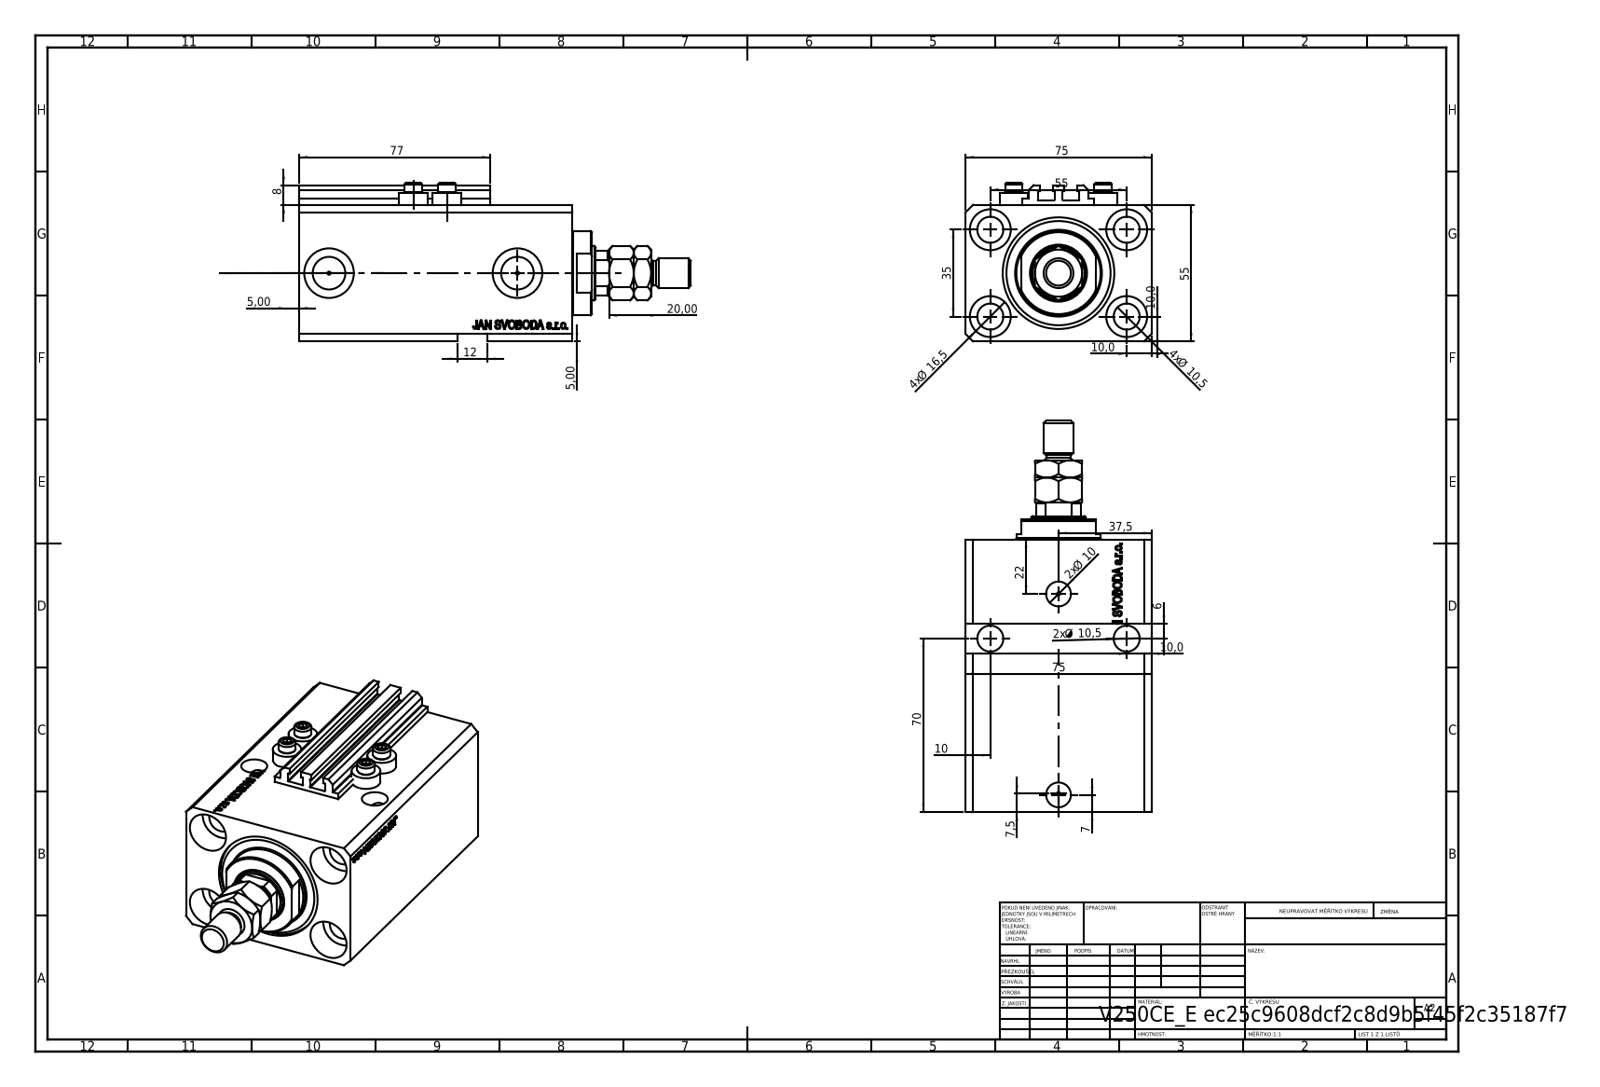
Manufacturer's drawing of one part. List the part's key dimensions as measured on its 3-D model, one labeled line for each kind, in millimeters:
Part name (STEP PRODUCT): V250CE_E; V250CE_C_VCP; ALLEN BOLT V250CE; V250CE_VC_E (+1 more)
STEP written by: SolidWorks 2019 (CONFIG_CONTROL_DESIGN)
Units: millimetres
Bodies: 9 solids, 1113 faces (529 planar, 130 cylindrical, 454 other)
Overall size (bounding box): 157.9 × 75 × 64
Volume: 394 729 mm³ · Surface area: 99 045 mm²
Round holes (diameter × count): ⌀10.5 ×7, ⌀1.25 ×4, ⌀4 ×4, ⌀16.5 ×4, ⌀10 ×2, ⌀13.16 ×2, ⌀20 ×2, ⌀22 ×1, ⌀32 ×1, ⌀45 ×1
Round bosses / shafts (diameter × count): ⌀11.6 ×4, ⌀7 ×4, ⌀34 ×1, ⌀12 ×1, ⌀10 ×1
Partial cylindrical surfaces — rounded edges, fillets, slot ends (radius × count): R0.2 ×10, R10.5 ×1
Main face-to-face distances: 55, 75, 110, 82.9, 27.1, 3, 9.9, 73, 100.1, 2.5
Hole centre spacings: 32.6, 55, 13.6, 14.09, 25.81, 32.87, 33.62, 35
